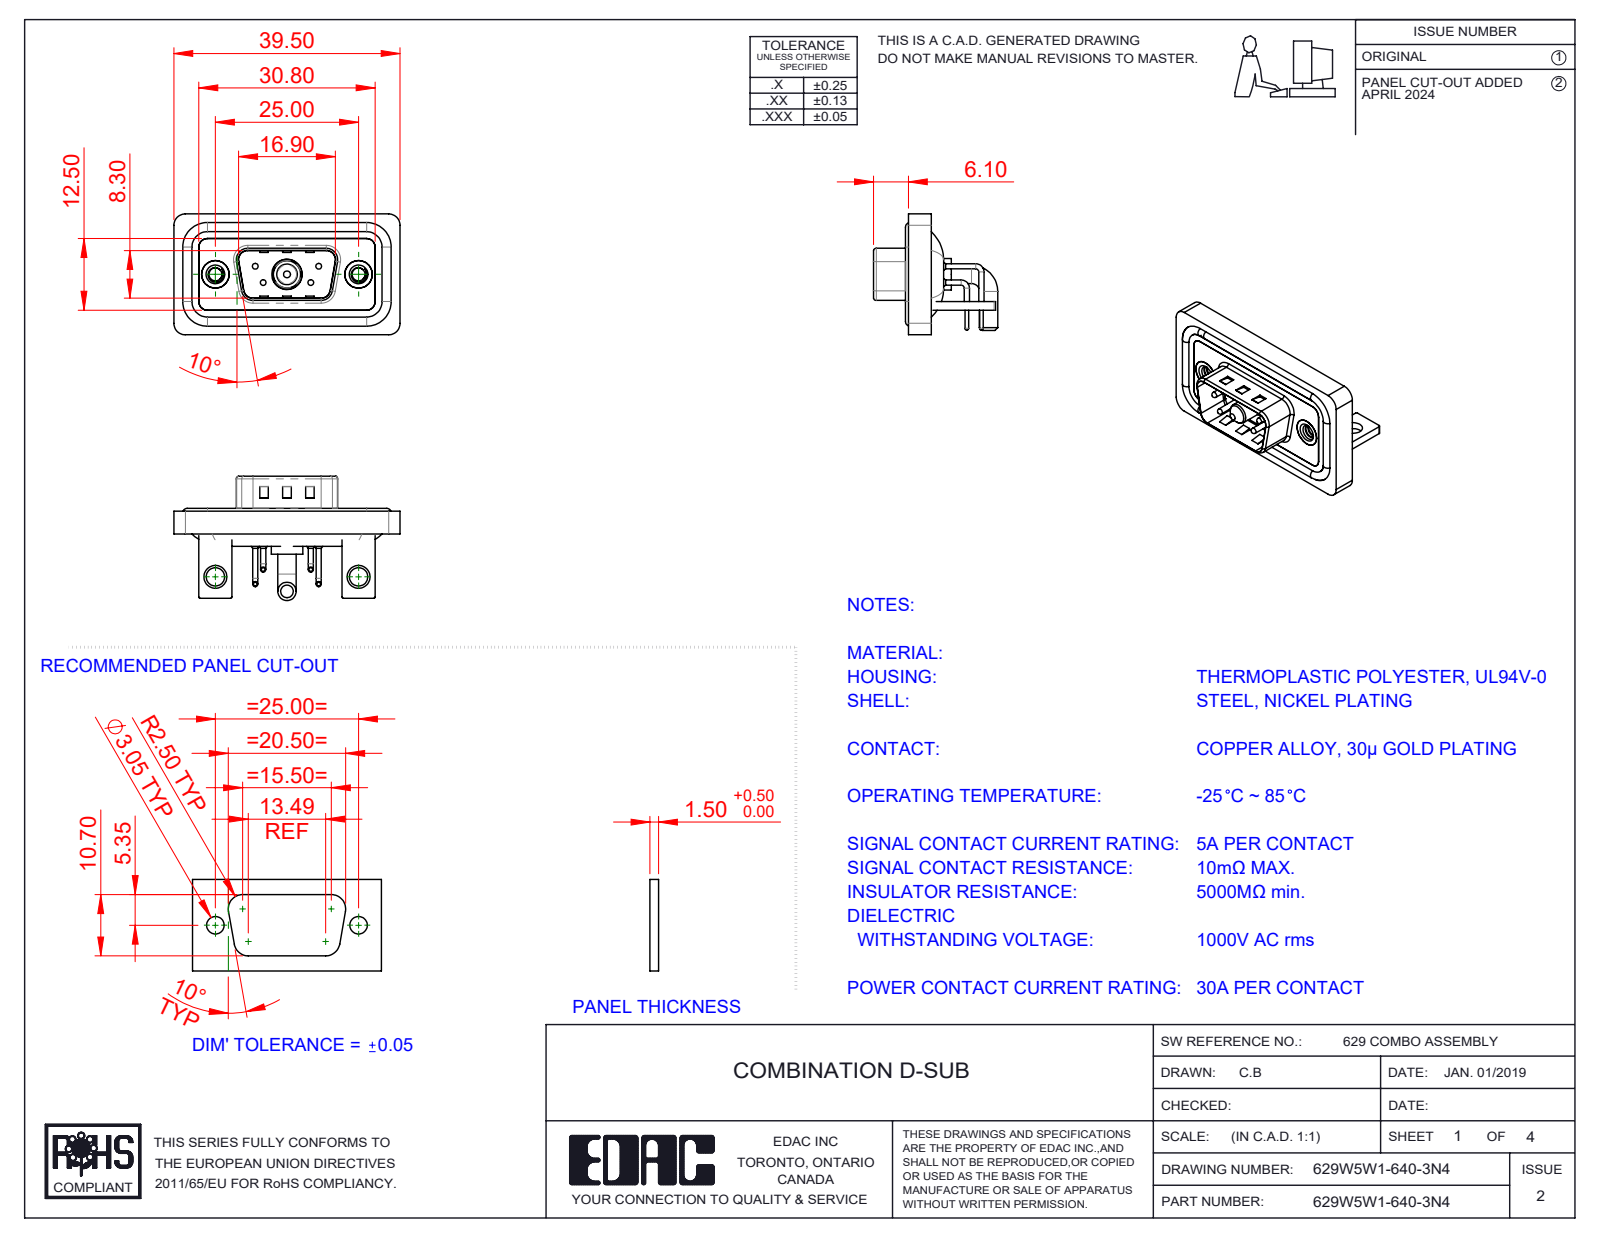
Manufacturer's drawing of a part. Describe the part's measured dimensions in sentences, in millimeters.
The part is named "629Combo Threaded Rivet_3; 629Combo Waterproof Housing_09 Contacts; 629Combo Housing_5W1; Power Pin_30A RA (+6 more)". Its 3-D file was written by "SolidWorks 2023 (CONFIG_CONTROL_DESIGN)". It is 15 solids with 934 faces: 431 planar, 363 cylindrical and 140 other. Overall it measures 39.5 by 21.7 by 21.1 millimeters. Its volume is 4 782 cubic millimeters and its surface area 7 769 square millimeters. Round holes: 4 of diameter 0.75, 4 of diameter 1.6, 4 of diameter 2, 2 of diameter 2.26, 2 of diameter 3.2, 2 of diameter 4, 2 of diameter 4.8, 2 of diameter 5, 1 of diameter 4.85, 1 of diameter 5.3. Round bosses or shafts: 8 of diameter 0.9, 4 of diameter 1.6, 4 of diameter 1.5, 4 of diameter 1, 4 of diameter 0.65, 2 of diameter 4.9, 2 of diameter 3.2, 1 of diameter 5.5. Partial cylindrical surfaces (rounded edges, fillets, slot ends): 19 of radius 2, 18 of radius 1.5, 16 of radius 0.25, 9 of radius 0.5, 8 of radius 1.6, 4 of radius 0.6, 4 of radius 0.65, 4 of radius 0.9. The main face-to-face distances are 0.4, 1.5, 0.8, 2.9, 1.1, 2.1, 1.2, 1.6, 2.5, 3.7. The hole center spacings are 3.16, 5.72, 7.1, 12.5, 18.1, 25, 4.39, 4.4.
